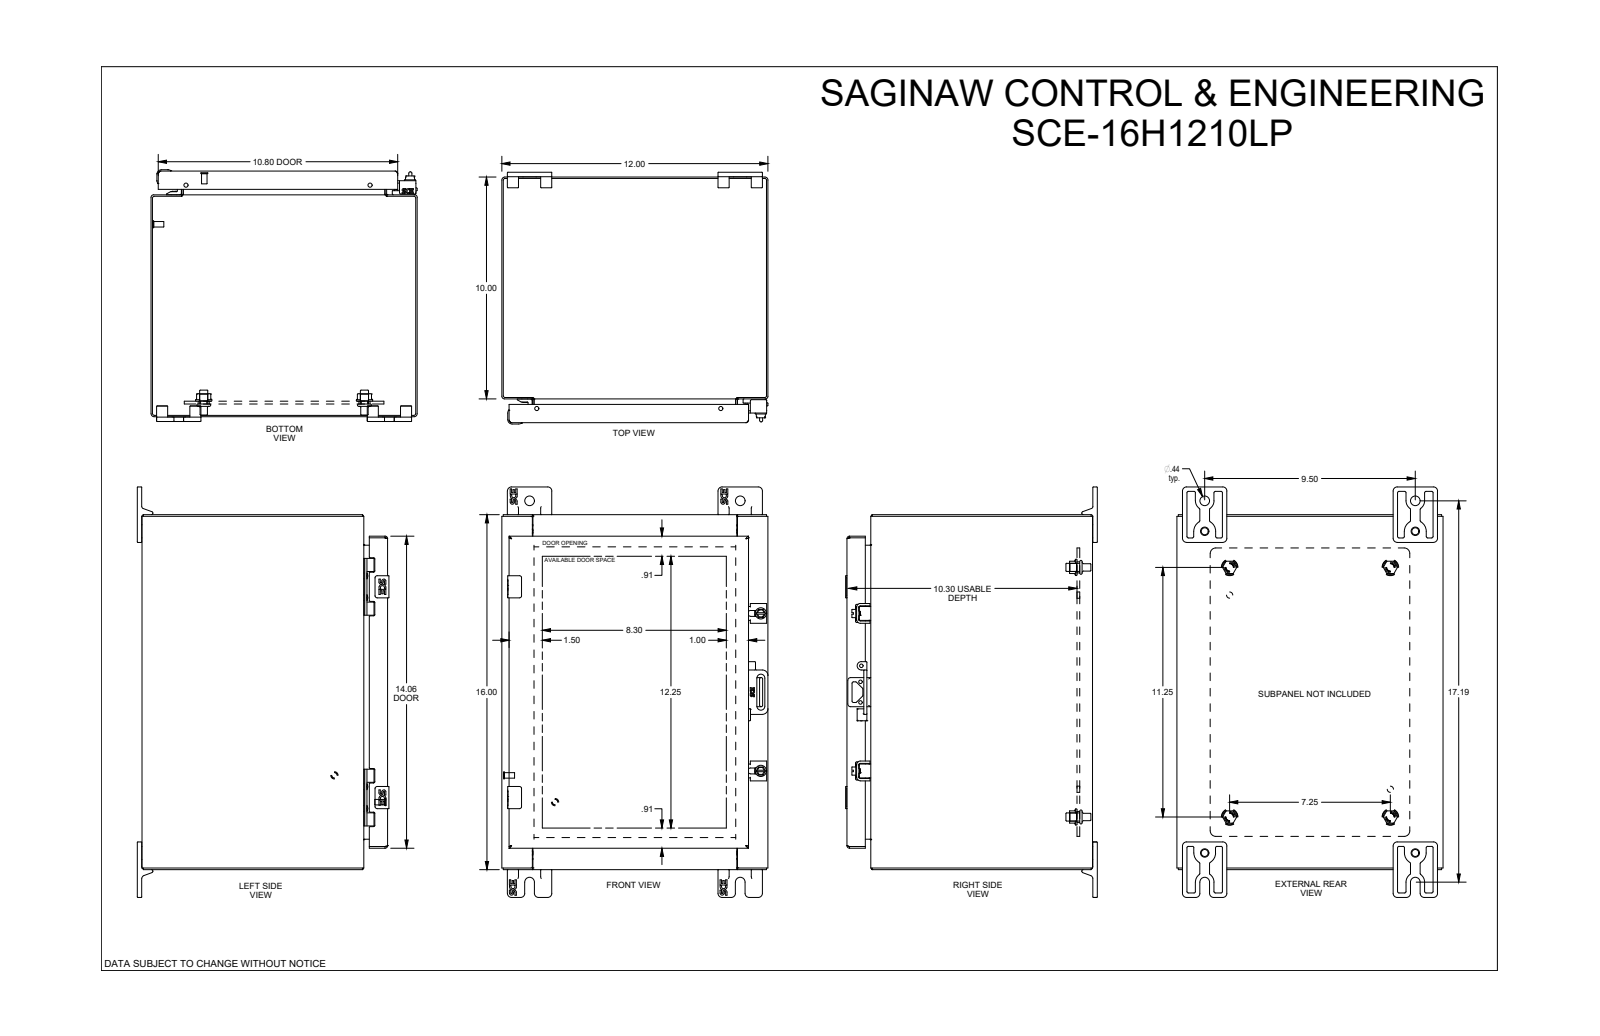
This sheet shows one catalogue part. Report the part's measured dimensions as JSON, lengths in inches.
{"part_name": "SCE-16H1210LP", "step_written_by": "SolidWorks 2019 (AUTOMOTIVE_DESIGN)", "units": "inches", "bodies": {"solids": 56, "faces": 3444, "planar": 1285, "cylindrical": 992, "other": 1167}, "overall_size": [18.5, 12, 11.348], "volume_in3": 104.5, "surface_area_in2": 2541, "round_holes": [[0.172, 4], [0.205, 4], [0.244, 4], [0.266, 4], [0.31, 4], [0.312, 4], [0.367, 4], [0.375, 4], [0.437, 4], [0.5, 4], [0.25, 3], [0.04, 2]], "round_bosses_or_shafts": [[0.17, 7], [0.25, 6], [0.248, 5], [0.59, 4], [0.376, 4], [0.366, 4], [0.332, 4], [0.24, 4]], "partial_cylinders_radius": [[0.025, 121], [0.01, 114], [0.015, 56], [0.063, 33], [0.03, 32], [0.06, 30], [0.062, 30], [0.185, 21]], "face_to_face_distances": [0.075, 11.925, 0.075, 15.925, 0.06, 10.998, 10.923, 12, 11.85, 11.058], "hole_center_spacings": [9.5, 0.02, 0.493, 0.985, 1.976, 8.531, 12.924, 15.359]}
